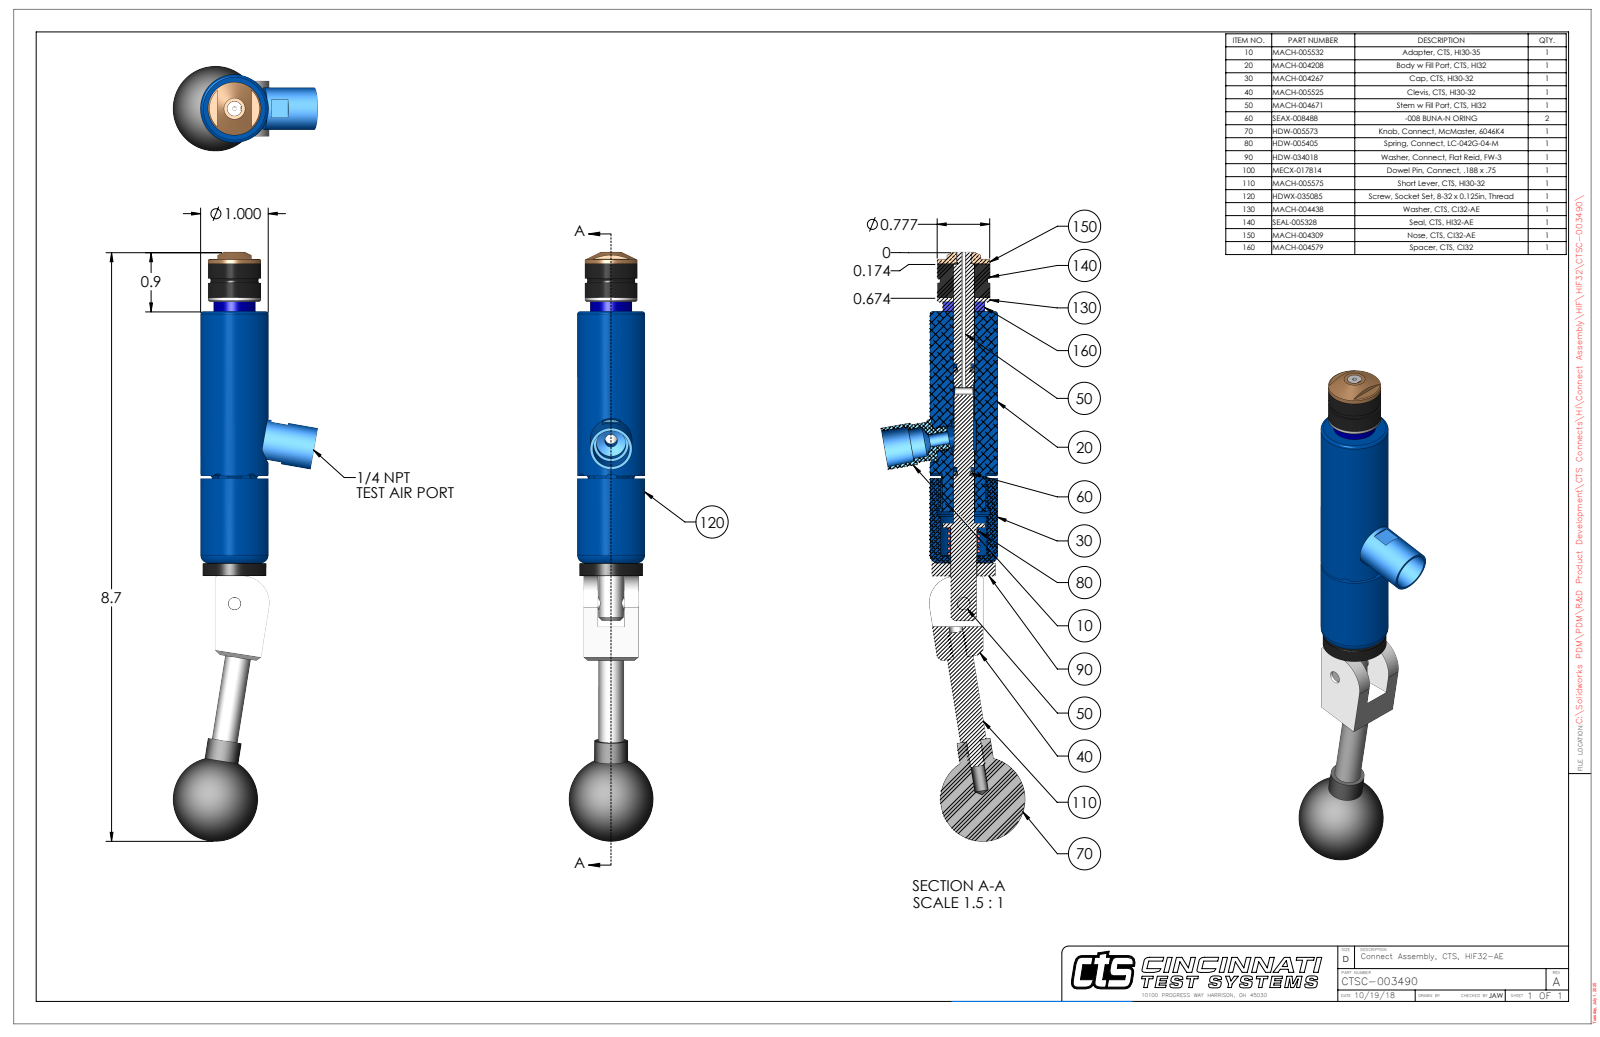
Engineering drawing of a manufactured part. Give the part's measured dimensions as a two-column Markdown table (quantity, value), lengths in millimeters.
| quantity | value |
| --- | --- |
| part name | CTSC-003490 |
| STEP written by | SolidWorks 2023 (AUTOMOTIVE_DESIGN) |
| units | millimeters |
| bodies | 10 solids, 282 faces (97 planar, 121 cylindrical, 64 other) |
| overall size | 221.1 × 54.1 × 31.8 |
| volume | 85 490 mm³ |
| surface area | 27 190 mm² |
| round holes (diameter × count) | 5.1 × 2, 1.6 × 1, 2.8 × 1, 3.5 × 1, 3.8 × 1, 4.7 × 1, 4.8 × 1, 5.4 × 1, 7.9 × 1, 8 × 1, 8 × 1, 9.8 × 1 |
| round bosses / shafts (diameter × count) | 6.4 × 2, 5.1 × 2, 25.4 × 1, 23.8 × 1, 19.7 × 1, 15.7 × 1, 15.7 × 1, 12.7 × 1 |
| partial cylindrical surfaces (radius × count) | 2.4 × 6, 0.7 × 2, 1.8 × 1, 8.3 × 1, 10.2 × 1, 11.8 × 1 |
| main face-to-face distances | 5.3, 15.3, 112.3, 12.7, 17.8, 94.5, 5.1, 99.6, 20.6, 117 |
| hole center spacings | 15.2, 42.1, 57.2 |
